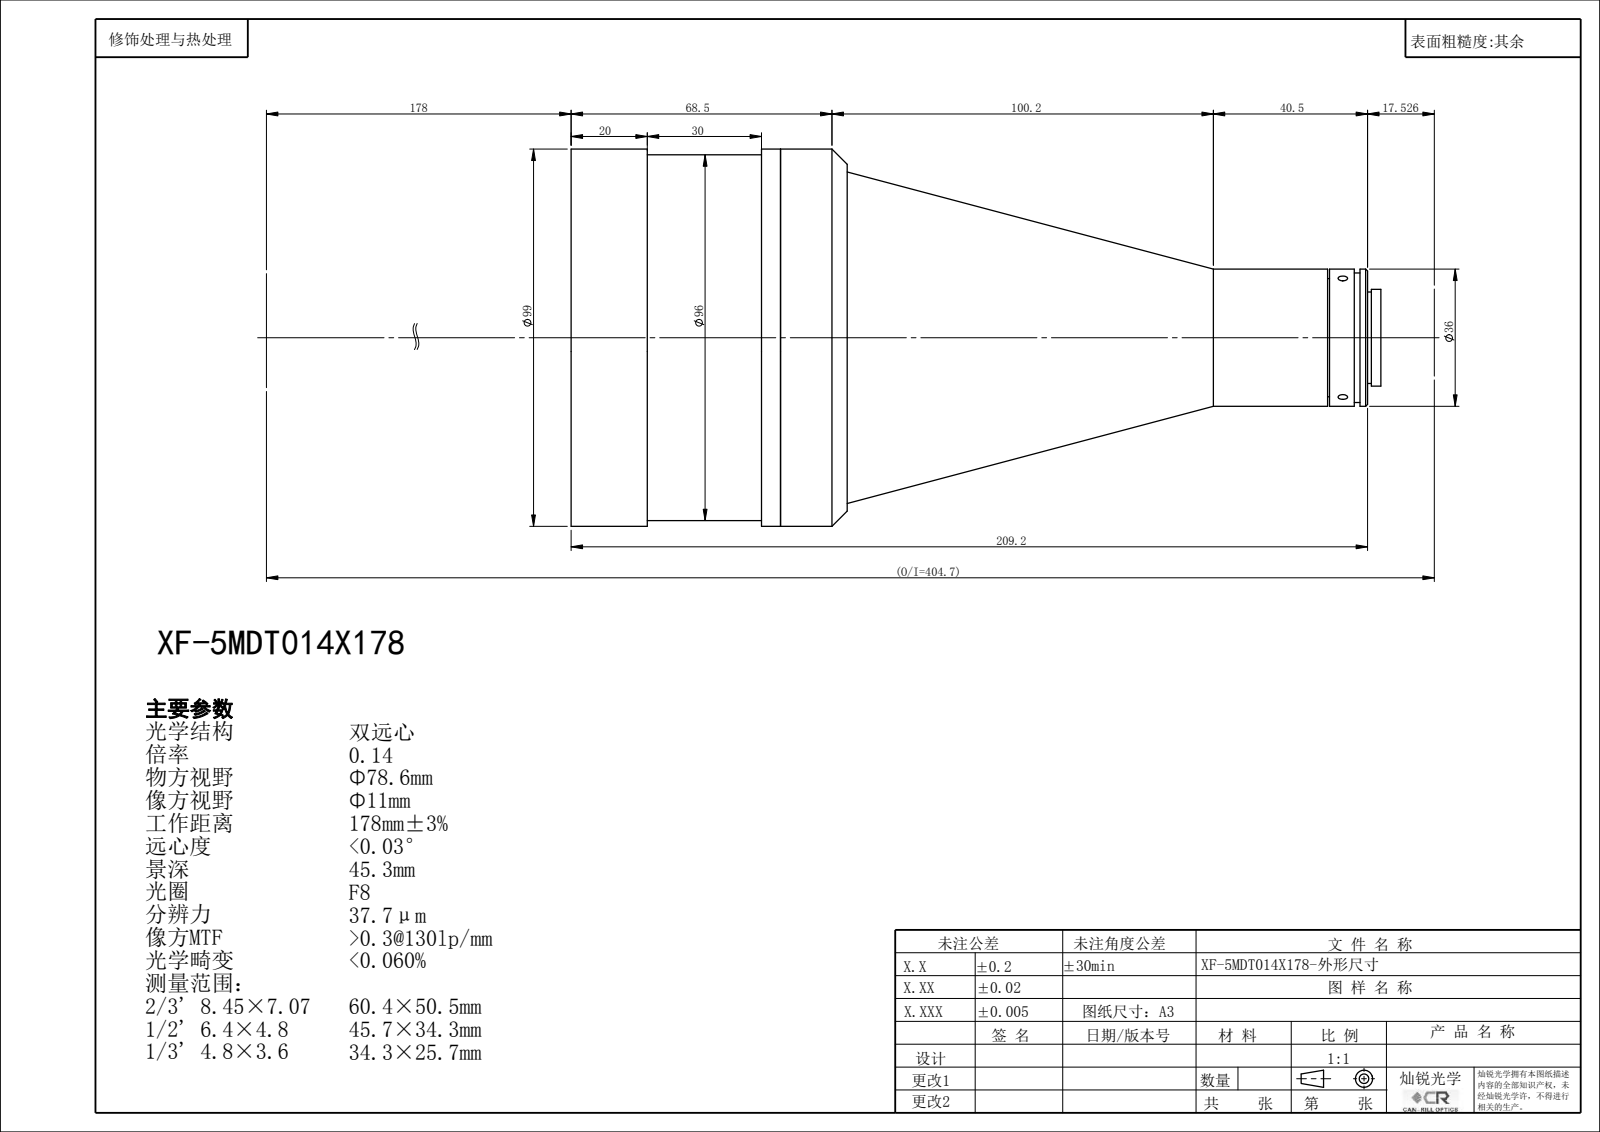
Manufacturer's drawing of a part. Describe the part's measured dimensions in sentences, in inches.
The part is named "XF-5MDT014X178". Its 3-D file was written by "SolidWorks 2014 (CONFIG_CONTROL_DESIGN)". It is 0 solids with 98 faces: 38 planar, 46 cylindrical and 14 other. Overall it measures 8.372 by 3.898 by 3.898 inches. Round holes: 4 of diameter 0.079, 3 of diameter 0.098, 1 of diameter 0.63, 1 of diameter 0.843, 1 of diameter 3.346, 1 of diameter 3.425, 1 of diameter 3.622. Round bosses or shafts: 1 of diameter 3.898, 1 of diameter 3.78, 1 of diameter 1.417, 1 of diameter 1.339, 1 of diameter 1, 1 of diameter 0.945. The main face-to-face distances are 2.165, 0.197, 0.375, 1.79, 2.854, 2.479, 0.689, 8.234, 7.859, 6.069. The hole center spacings are 0.453, 0.64, 0.906.
